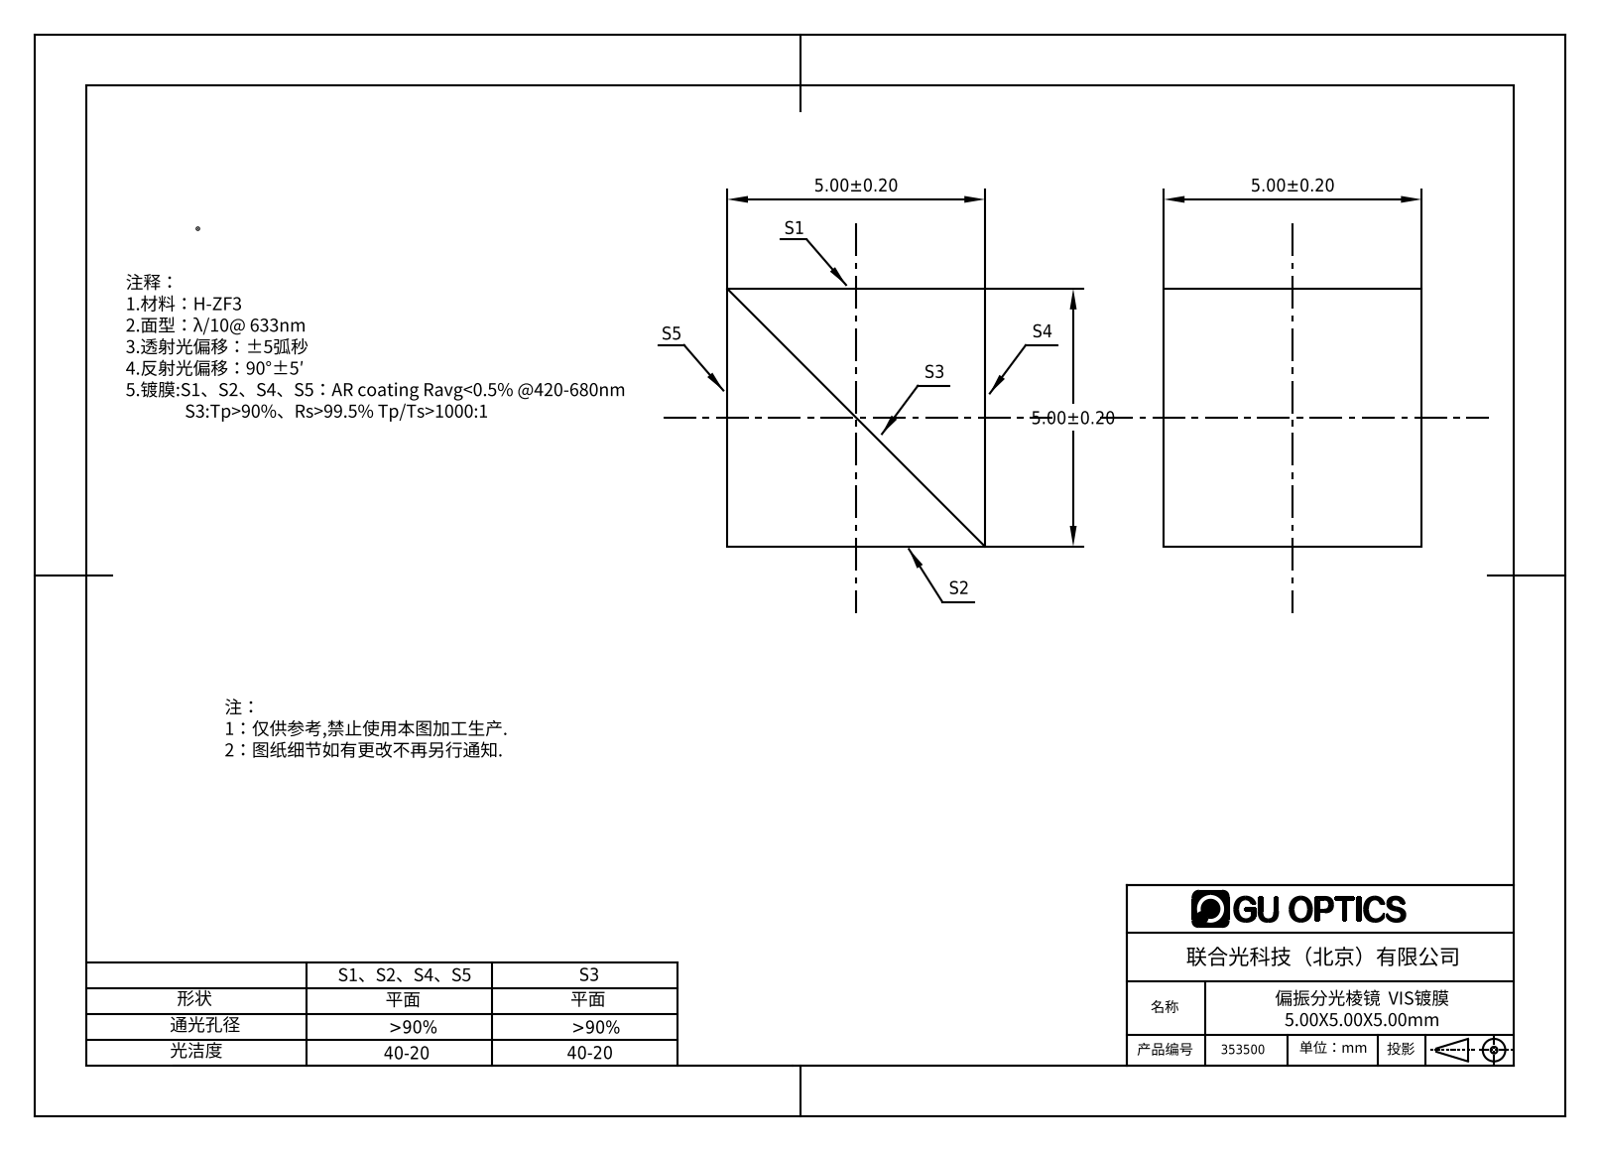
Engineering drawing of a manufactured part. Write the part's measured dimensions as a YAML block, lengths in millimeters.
part_name: "352500"
step_written_by: "SolidWorks 2016 (AUTOMOTIVE_DESIGN)"
units: millimeters
bodies: {solids: 2, faces: 10, planar: 10, cylindrical: 0, other: 0}
overall_size: [5, 5, 5]
volume: 125
surface_area: 221
face_to_face_distances: [5]
